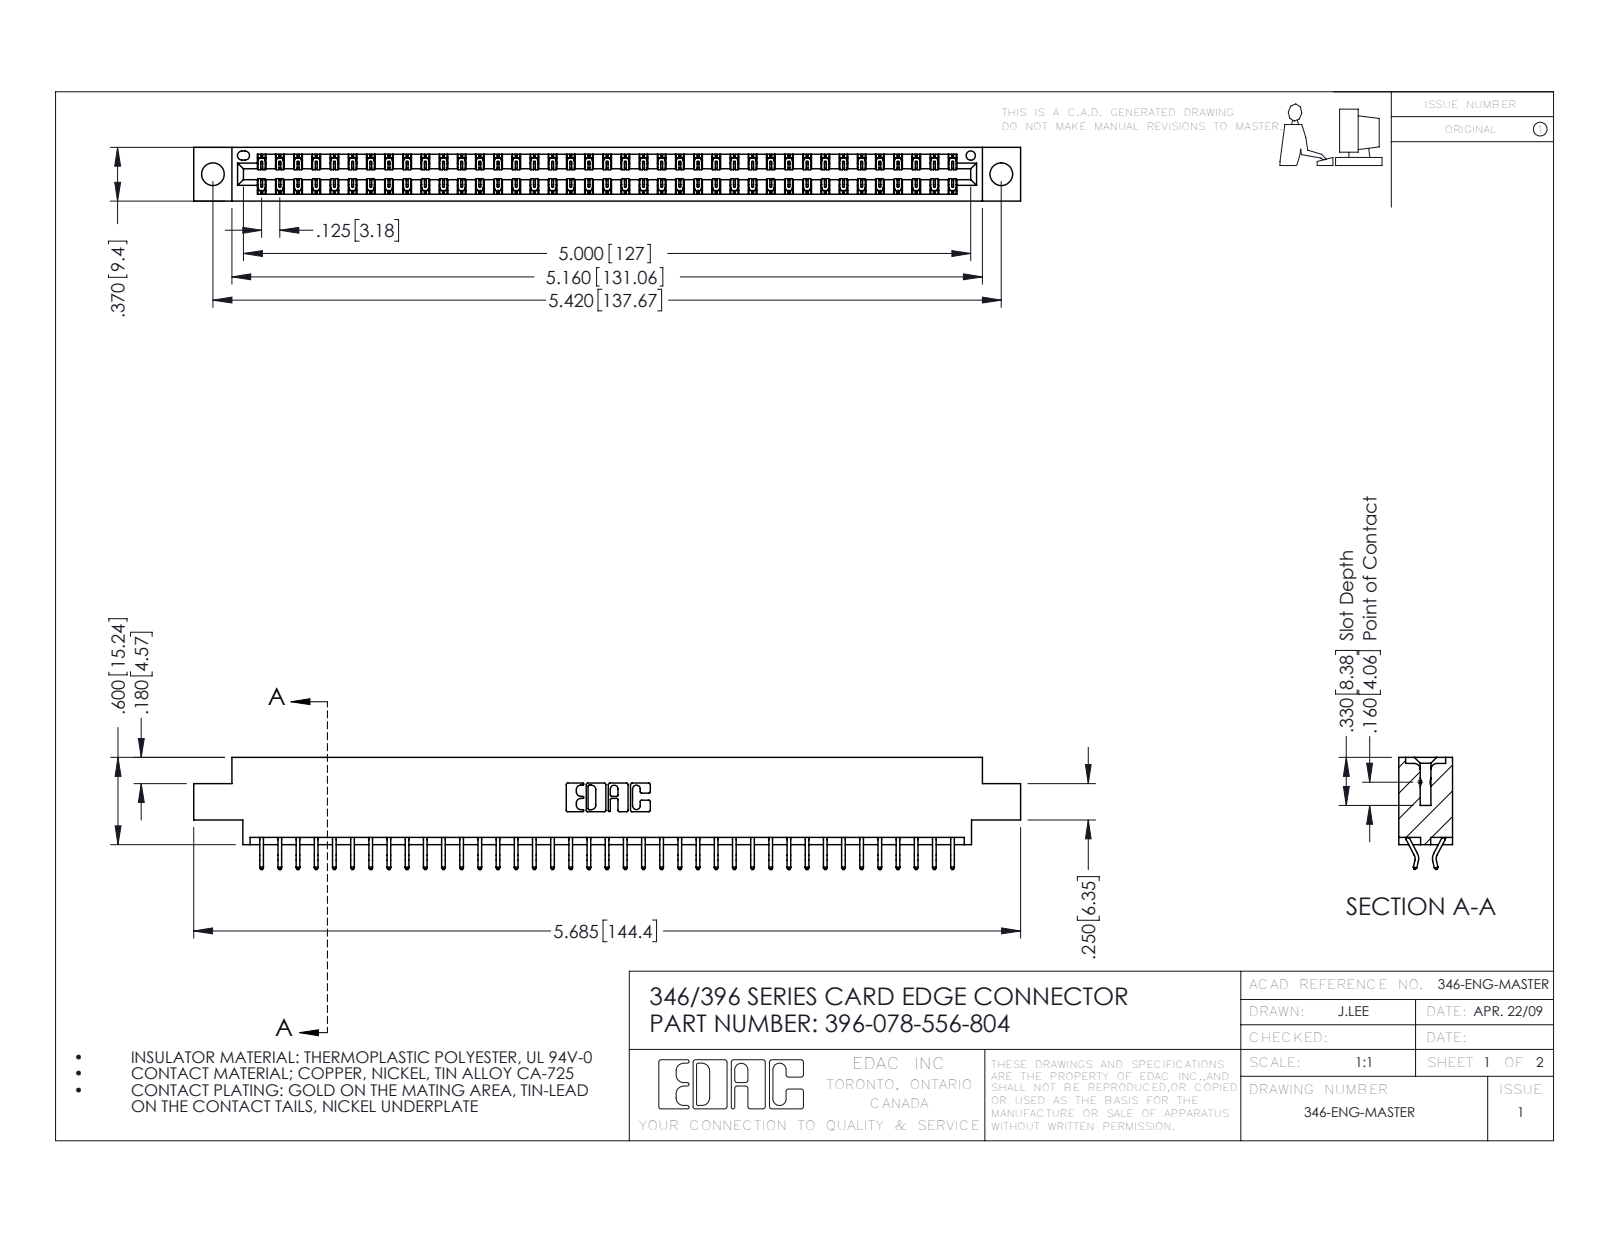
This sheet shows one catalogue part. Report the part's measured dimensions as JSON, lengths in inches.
{"part_name": "345-292-001_556 Tail; 396-078-556-804; 346 Part_0.170 Offset - 0.156 Dia-TH", "step_written_by": "SolidWorks 2016 (CONFIG_CONTROL_DESIGN)", "units": "inches", "bodies": {"solids": 79, "faces": 4650, "planar": 3122, "cylindrical": 1528, "other": 0}, "overall_size": [5.685, 0.77, 0.37], "volume_in3": 0.843, "surface_area_in2": 29.23, "round_holes": [[0.156, 2], [0.064, 1]], "partial_cylinders_radius": [[0.006, 117], [0.01, 22], [0.007, 6], [0.031, 6], [0.026, 3], [0.01, 2], [0.014, 2], [0.022, 2]], "face_to_face_distances": [0.048, 0.322, 0.37, 0.25, 0.025, 0.072, 0.298, 0.275, 0.148, 0.222], "hole_center_spacings": [0.246, 5.211, 5.42]}
